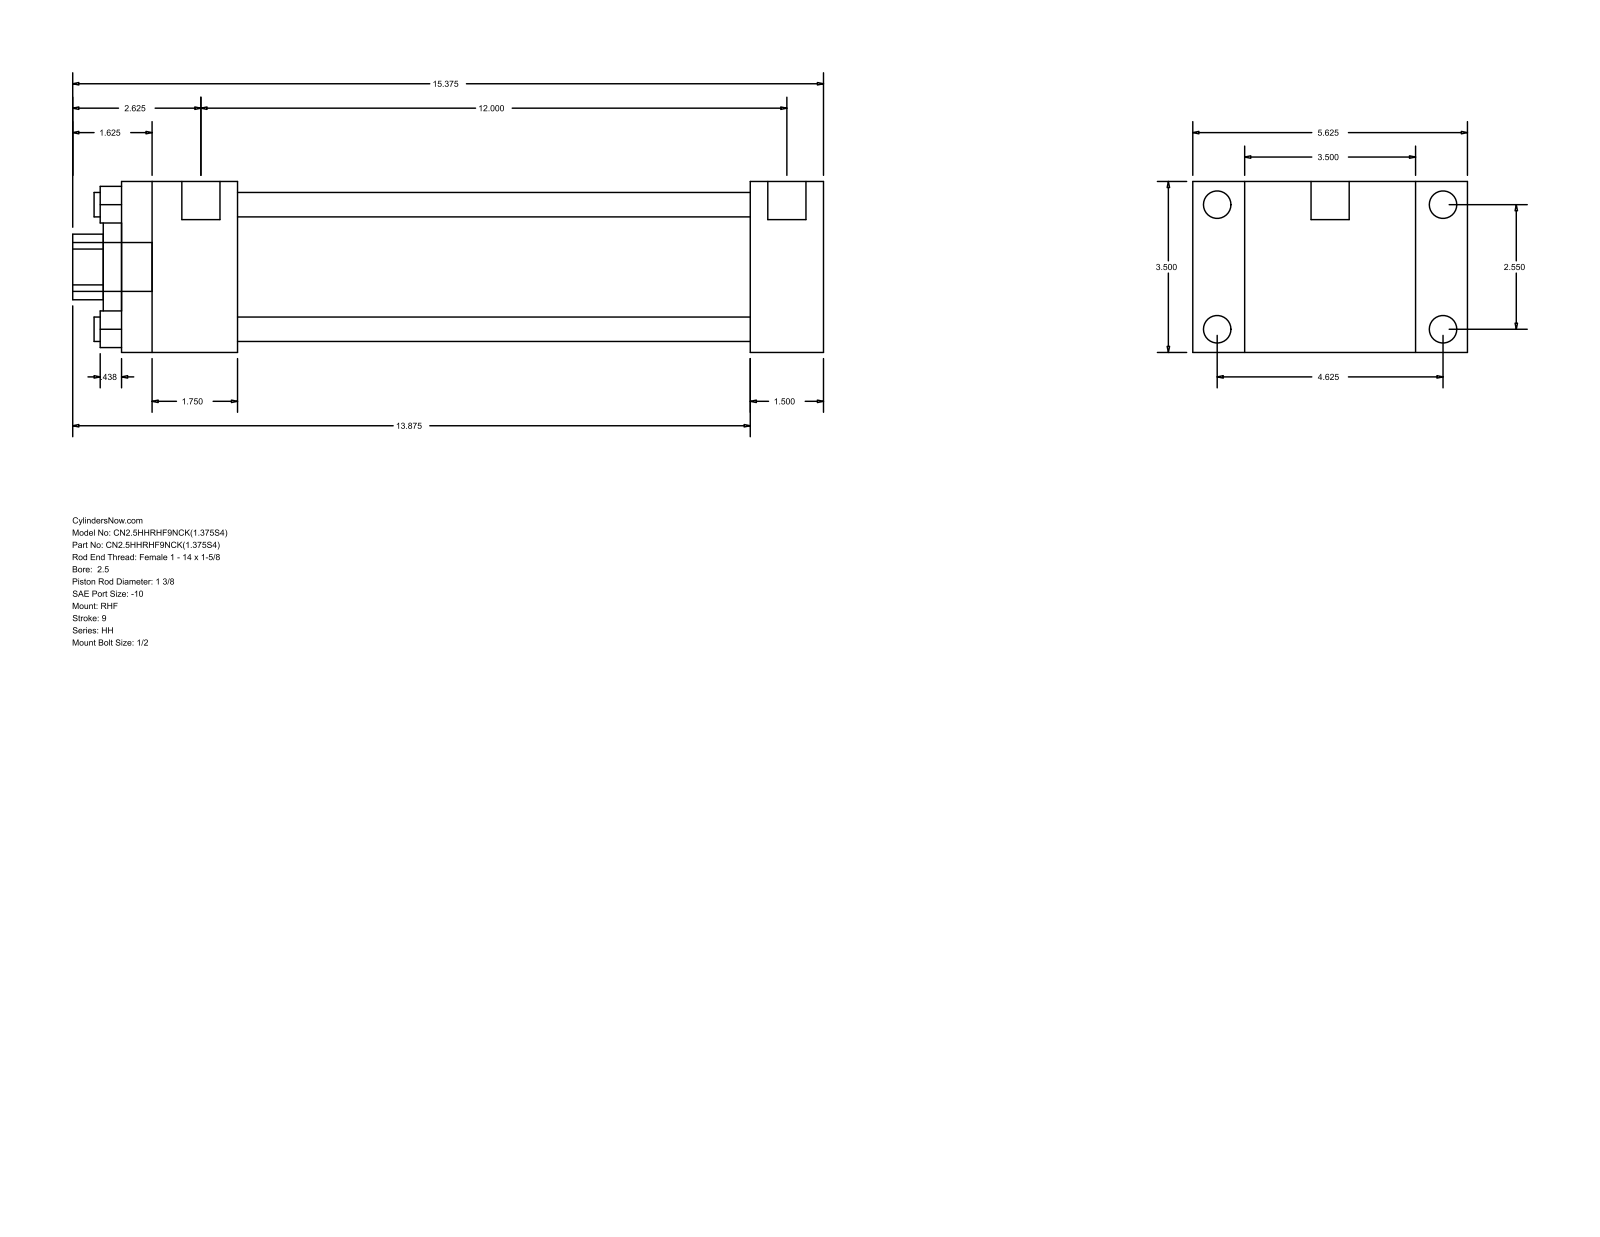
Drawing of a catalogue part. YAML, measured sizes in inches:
part_name: "HH_RHF__0250_1.375"
step_written_by: "GSSL Pune (CONFIG_CONTROL_DESIGN)"
units: inches
bodies: {solids: 0, faces: 88, planar: 60, cylindrical: 28, other: 0}
overall_size: [15.375, 5.625, 3.5]
round_holes:
  - {diameter: 0.5, count: 4}
  - {diameter: 1.375, count: 1}
  - {diameter: 2, count: 1}
  - {diameter: 2.875, count: 1}
round_bosses_or_shafts:
  - {diameter: 0.563, count: 4}
  - {diameter: 0.219, count: 4}
  - {diameter: 0.781, count: 2}
  - {diameter: 1, count: 1}
partial_cylinders:
  - {radius: 0.672, count: 1}
face_to_face_distances: [3.5, 1.5, 1.063, 4.563, 12.875, 14.375, 5.625, 2.375, 10.5, 12]
hole_center_spacings: [1.803, 2.55, 3.606]
